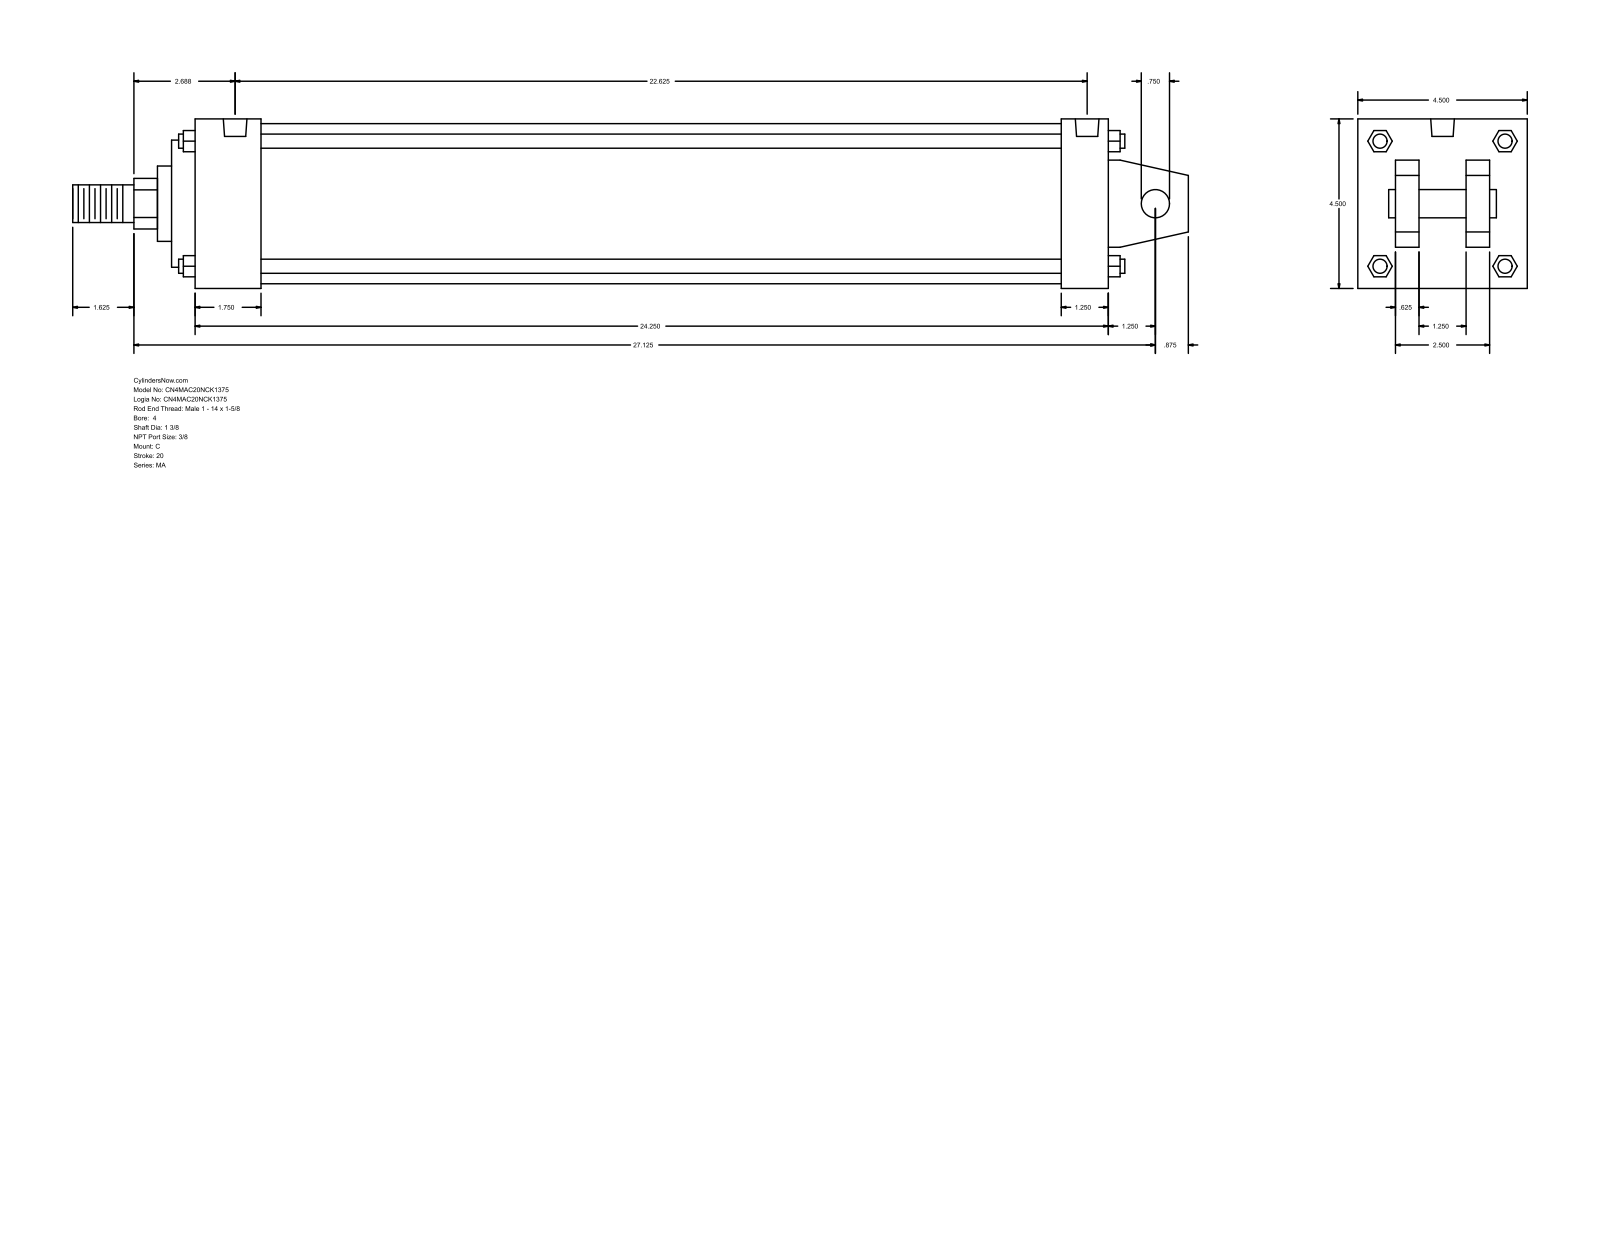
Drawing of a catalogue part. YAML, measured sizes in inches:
part_name: "MA_C__0400_1.375"
step_written_by: "GSSL Pune (CONFIG_CONTROL_DESIGN)"
units: inches
bodies: {solids: 0, faces: 141, planar: 109, cylindrical: 32, other: 0}
overall_size: [29.625, 4.5, 4.5]
round_holes:
  - {diameter: 0.437, count: 4}
  - {diameter: 0.627, count: 2}
round_bosses_or_shafts:
  - {diameter: 0.375, count: 4}
  - {diameter: 4.25, count: 1}
  - {diameter: 3.375, count: 1}
  - {diameter: 2, count: 1}
  - {diameter: 1.375, count: 1}
  - {diameter: 1, count: 1}
  - {diameter: 0.75, count: 1}
partial_cylinders:
  - {radius: 0.672, count: 1}
face_to_face_distances: [4.5, 0.625, 24.25, 2.875, 1.625, 1, 3.5, 1.875, 24.875, 23.625]
hole_center_spacings: [0.188, 22.25, 22.437, 22.625]
